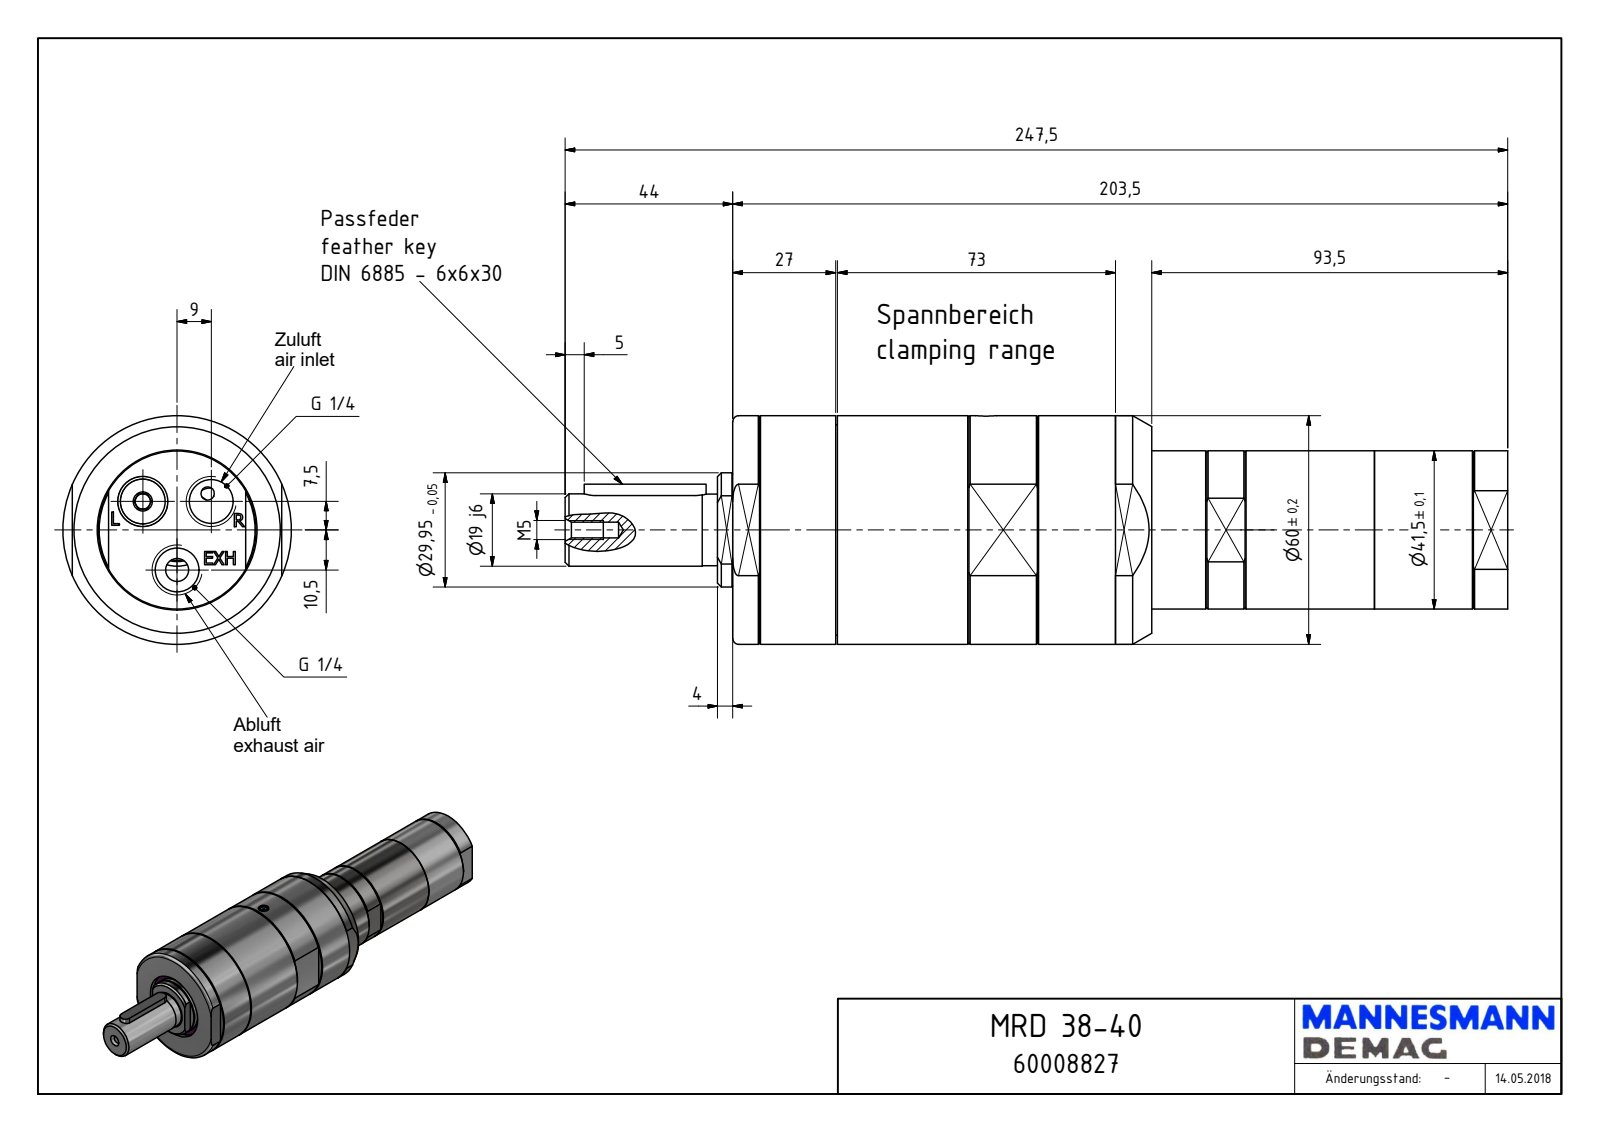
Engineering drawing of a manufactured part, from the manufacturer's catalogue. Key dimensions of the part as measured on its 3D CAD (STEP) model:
Part name (STEP PRODUCT): MRD 38-40_60008827
STEP written by: Autodesk Inventor 2018 (AUTOMOTIVE_DESIGN)
Units: millimetres
Bodies: 1 solid, 507 faces (221 planar, 235 cylindrical, 51 other)
Overall size (bounding box): 247.5 × 60 × 60
Volume: 441 403 mm³ · Surface area: 50 231 mm²
Round holes (diameter × count): ⌀11.45 ×3, ⌀4 ×2, ⌀1.55 ×1, ⌀4.13 ×1, ⌀5.5 ×1, ⌀35 ×1, ⌀40 ×1, ⌀42 ×1, ⌀55.38 ×1
Round bosses / shafts (diameter × count): ⌀60 ×1, ⌀55.18 ×1, ⌀50.18 ×1, ⌀41.5 ×1, ⌀37.33 ×1, ⌀29.95 ×1, ⌀19 ×1, ⌀18.8 ×1
Partial cylindrical surfaces — rounded edges, fillets, slot ends (radius × count): R11.68 ×94, R3 ×2, R24.64 ×1, R24.96 ×1
Main face-to-face distances: 93.5, 203.5, 110, 55, 1, 9.5, 6.5, 107.5, 2.82, 107.18
Hole centre spacings: 11.72, 20.12, 10.5, 18
